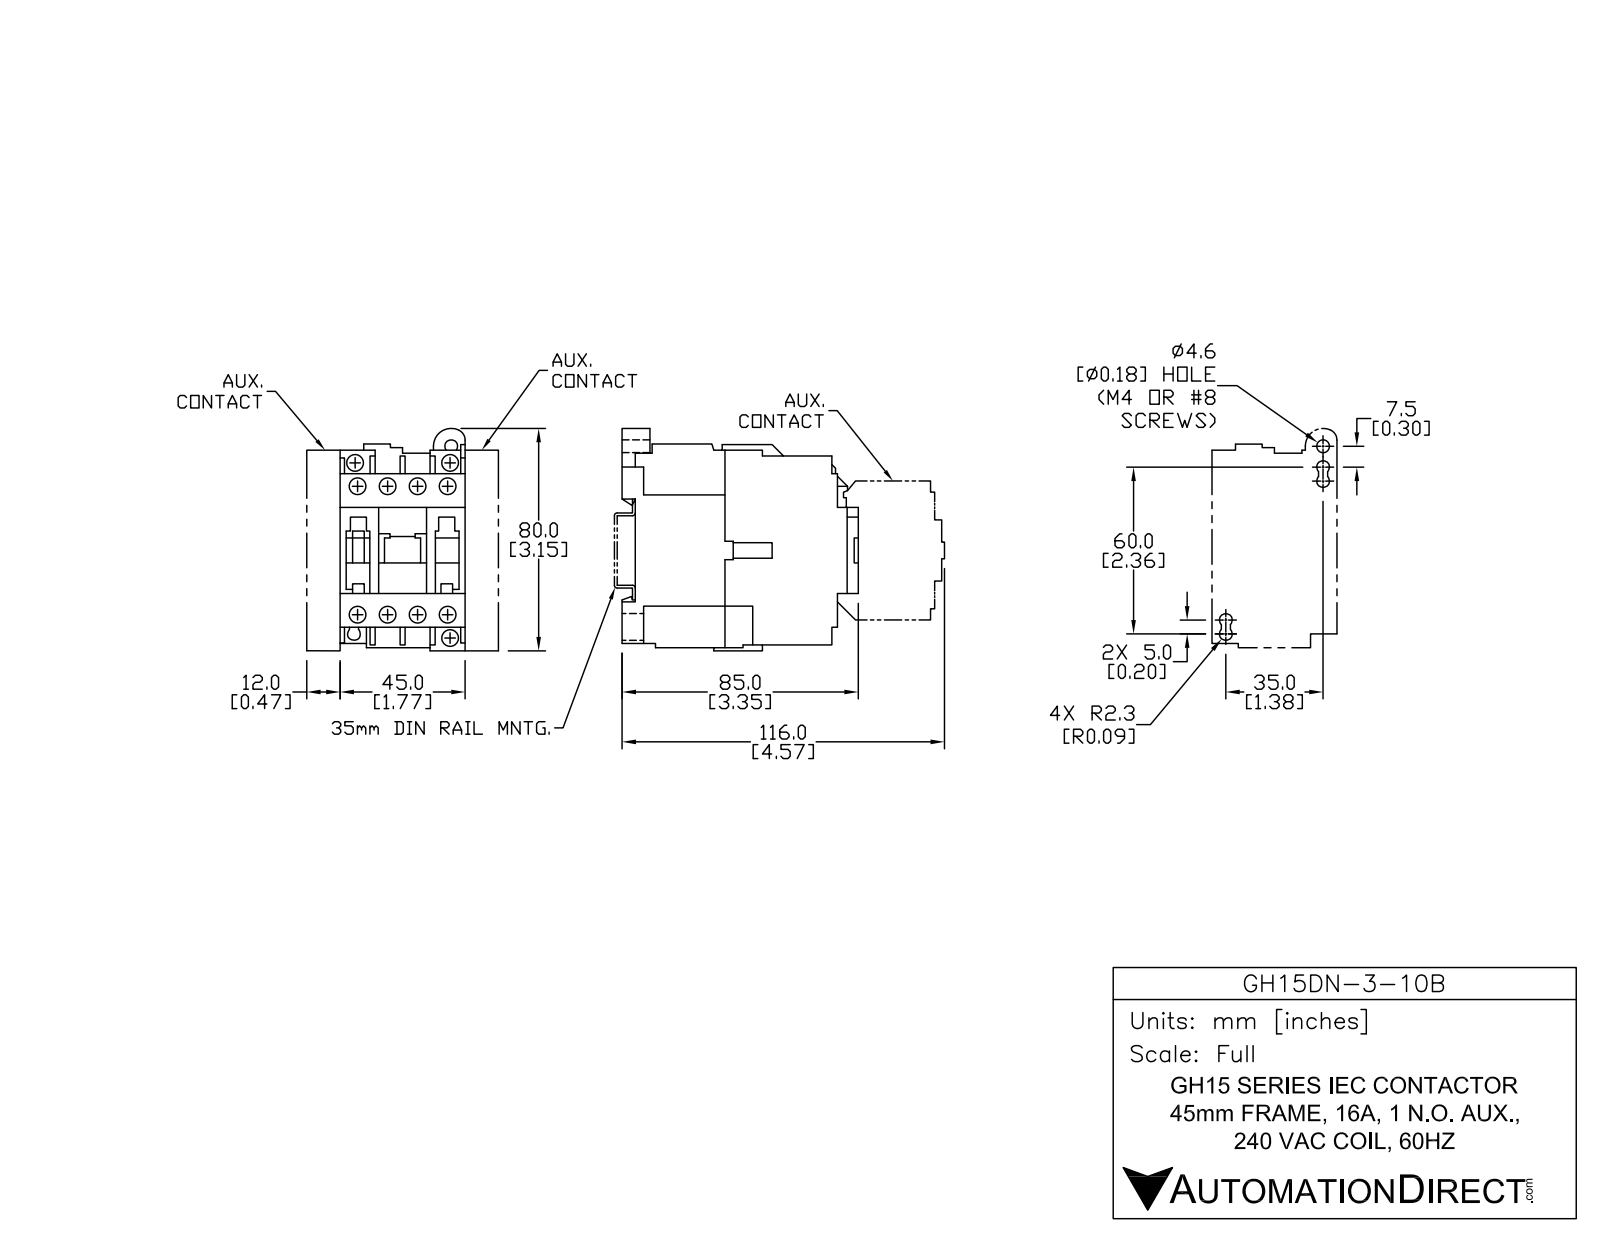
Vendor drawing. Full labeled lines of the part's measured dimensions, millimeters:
Part name (STEP PRODUCT): GH15DN-3-10B
STEP written by: SolidWorks 2009 (AUTOMOTIVE_DESIGN)
Units: millimetres
Bodies: 1 solid, 666 faces (447 planar, 65 cylindrical, 154 other)
Overall size (bounding box): 85.5 × 80 × 45
Volume: 196 351 mm³ · Surface area: 35 792 mm²
Round holes (diameter × count): ⌀6.25 ×9, ⌀6.5 ×2, ⌀4.6 ×1
Partial cylindrical surfaces — rounded edges, fillets, slot ends (radius × count): R1 ×10, R2.3 ×8, R4.75 ×8, R3 ×2, R4.99 ×1, R5 ×1
Main face-to-face distances: 45, 9.5, 35.5, 12.12, 23.38, 8, 7, 33.75, 10.38, 32.87
Hole centre spacings: 11.25, 47.12, 22.5, 45.76, 50.99, 7.62, 33.75, 53.38
